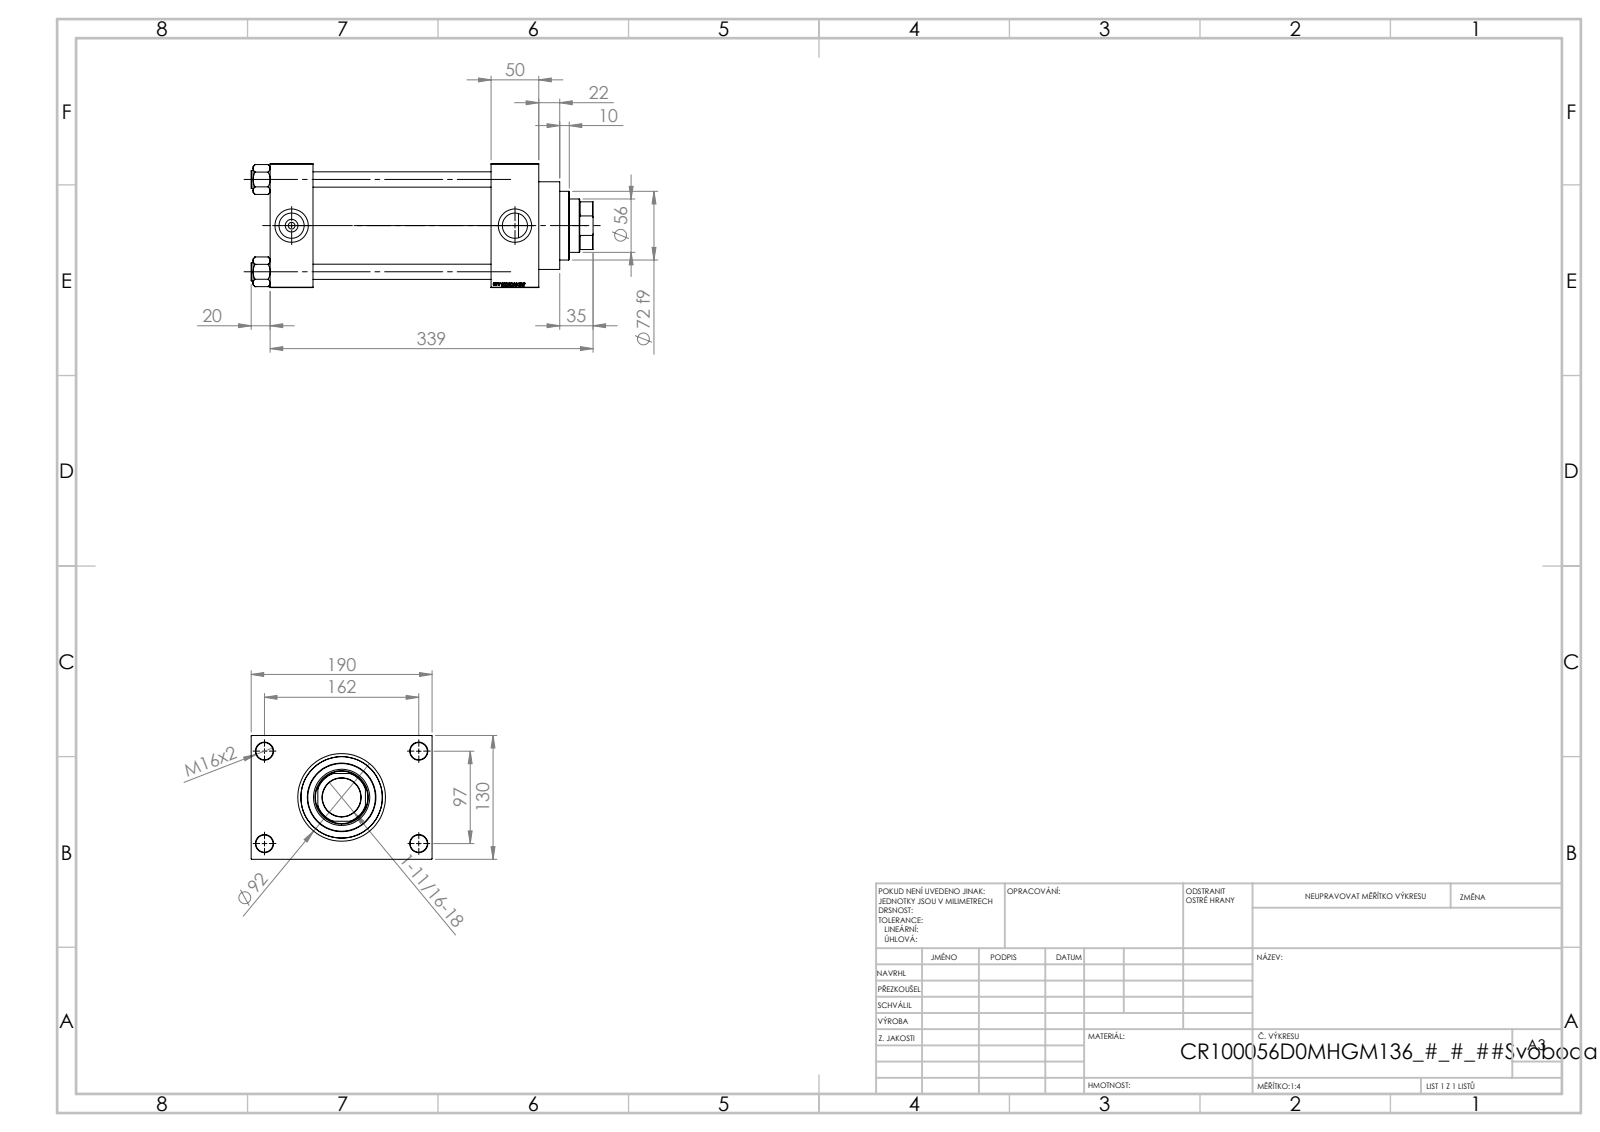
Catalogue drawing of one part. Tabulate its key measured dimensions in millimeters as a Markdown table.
| quantity | value |
| --- | --- |
| part name | V215_VC_A; V215CR_VCP_D; NUT_M5_D; V215CR_D_Body (+1 more) |
| STEP written by | SolidWorks 2019 (CONFIG_CONTROL_DESIGN) |
| units | millimeters |
| bodies | 11 solids, 1151 faces (545 planar, 88 cylindrical, 518 other) |
| overall size | 359 × 190 × 130 |
| volume | 3 120 000 mm³ |
| surface area | 481 166 mm² |
| round holes (diameter × count) | 16 × 4, 18 × 4, 7 × 2, 26.44 × 2, 35 × 2, 40.5 × 1, 56 × 1, 59 × 1, 76 × 1, 85.5 × 1, 100 × 1 |
| round bosses / shafts (diameter × count) | 19 × 4, 106 × 1, 92 × 1, 72 × 1 |
| partial cylindrical surfaces (radius × count) | 27 × 1 |
| main face-to-face distances | 130, 50, 45, 187, 232, 282, 237, 30, 160, 190 |
| hole center spacings | 32.55, 68.52, 94.41, 96.9, 102.27, 129.45, 161.73, 97 |
